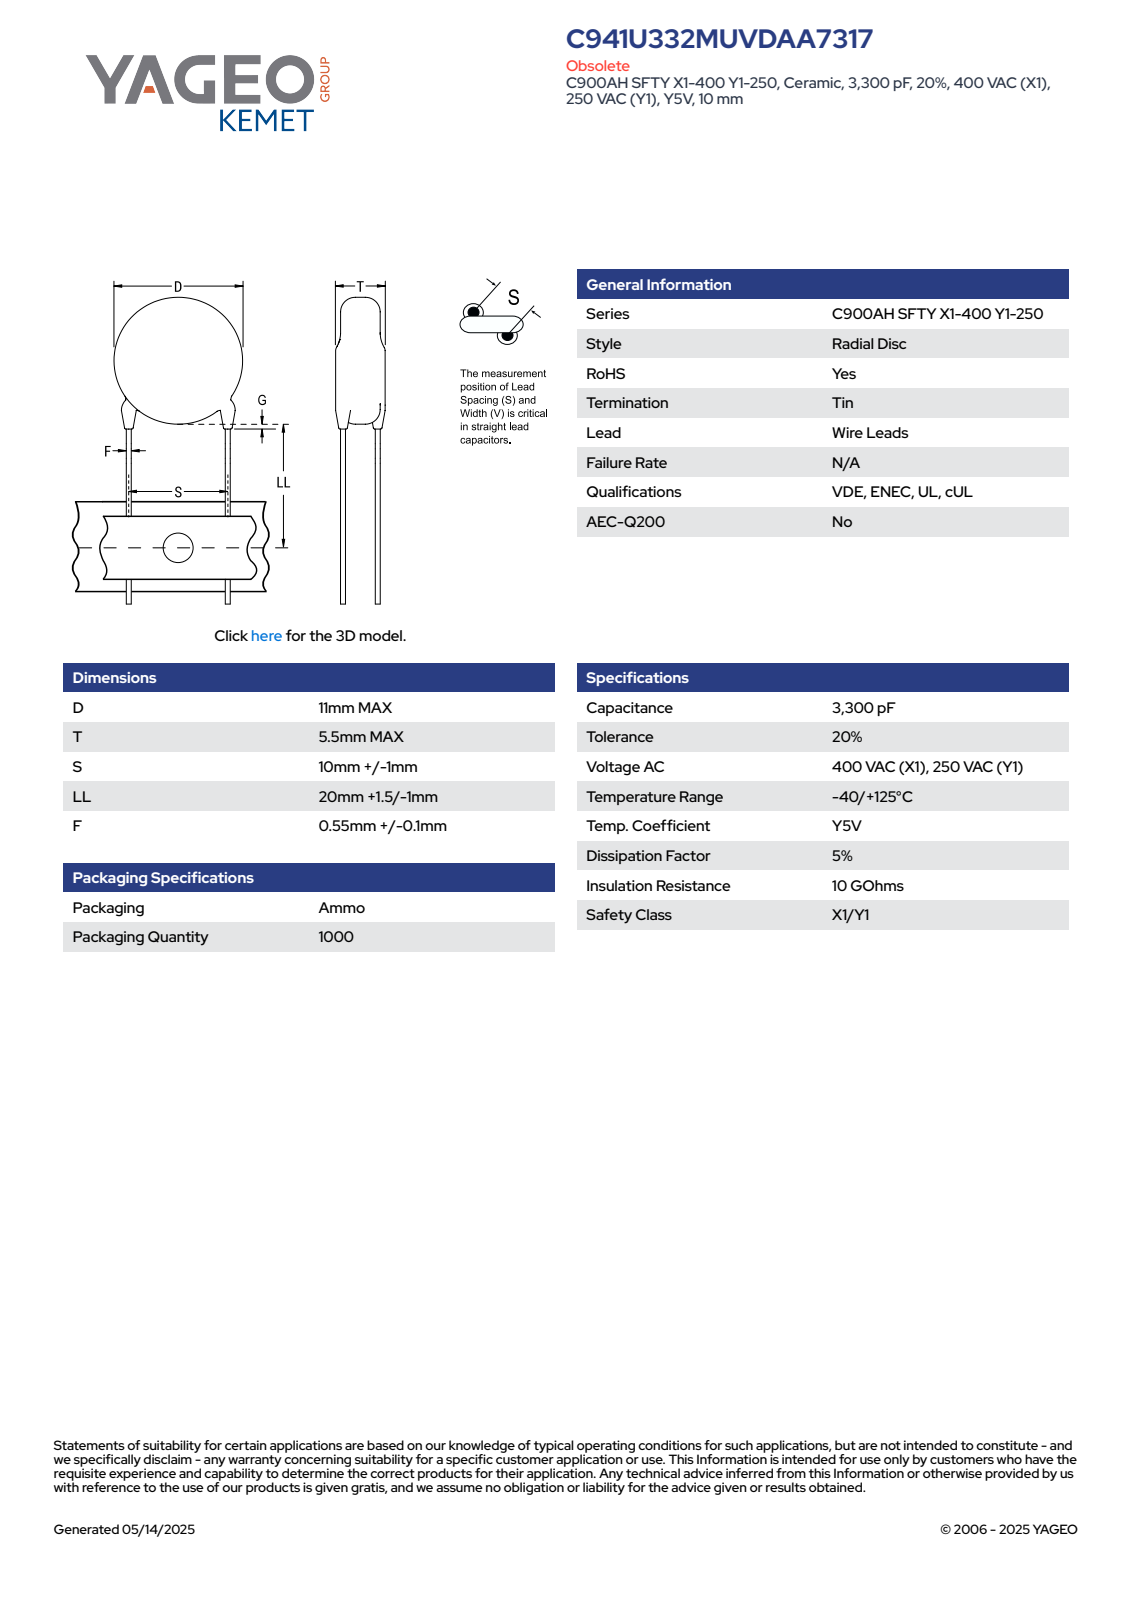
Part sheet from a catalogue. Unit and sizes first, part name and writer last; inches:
Units: inches
Overall size (bounding box): 1.28 × 0.433 × 0.217
Round bosses / shafts (diameter × count): ⌀0.026 ×2, ⌀0.433 ×1
Main face-to-face distances: 0.217, 0.05, 1.088, 1.038, 0.014, 0.041, 0.204, 0.031, 0.148, 0.154
Volume: 0.032 in³ · Surface area: 0.708 in²
Bodies: 4 solids, 83 faces (61 planar, 6 cylindrical, 16 other)
Part name (STEP PRODUCT): CCD_STC900_D11T5.5S10LL21.5F0.65G3
STEP written by: SolidWorks 2014 (AUTOMOTIVE_DESIGN)
